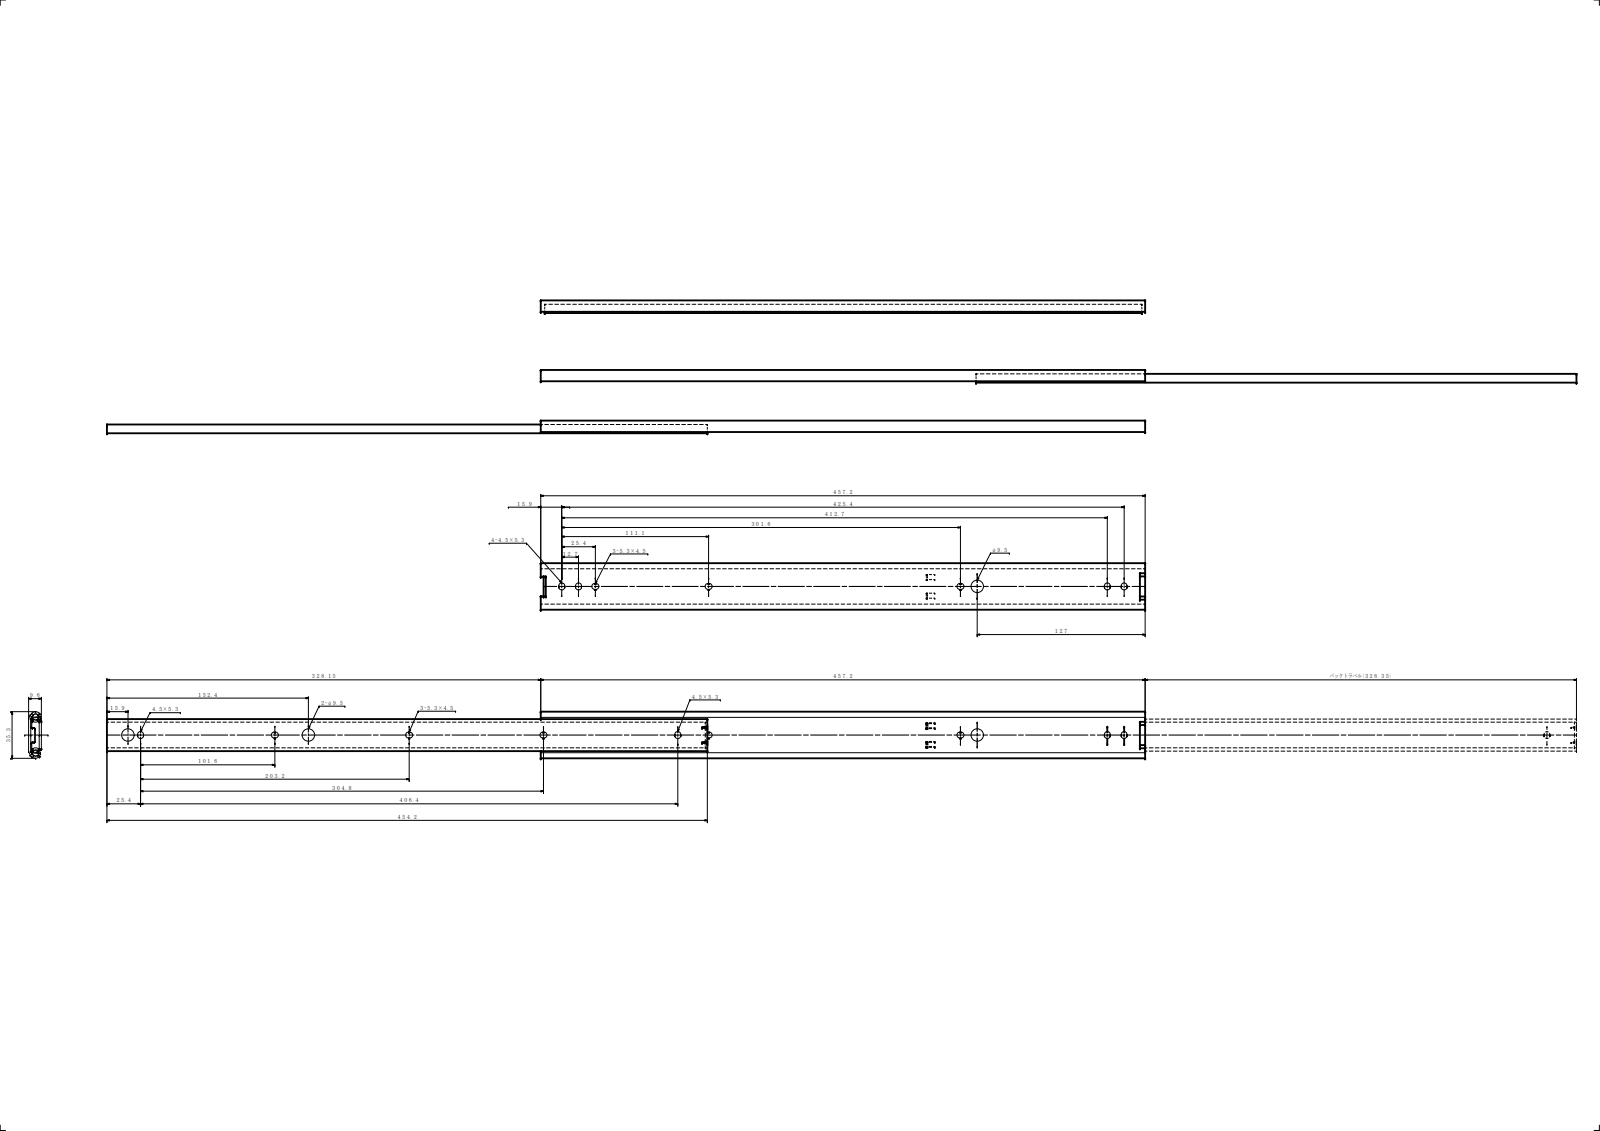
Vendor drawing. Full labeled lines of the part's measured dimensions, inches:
Part name (STEP PRODUCT): IM 3520-18; OM 3520-18; 3520-18
STEP written by: SolidWorks 2019 (CONFIG_CONTROL_DESIGN)
Units: inches
Bodies: 2 solids, 147 faces (72 planar, 75 cylindrical, 0 other)
Overall size (bounding box): 30.919 × 1.39 × 0.378
Volume: 3.483 in³ · Surface area: 116.3 in²
Round holes (diameter × count): ⌀0.374 ×3
Partial cylindrical surfaces — rounded edges, fillets, slot ends (radius × count): R0.089 ×26, R0.016 ×6, R0.039 ×4, R0.098 ×4, R0.118 ×4, R0.008 ×2, R0.071 ×2, R0.079 ×2
Main face-to-face distances: 0.063, 0.315, 0.378, 0.252, 0.051, 0.264, 0.114, 0.201, 0.184, 0.121
Hole centre spacings: 5.374, 19.919, 25.293
